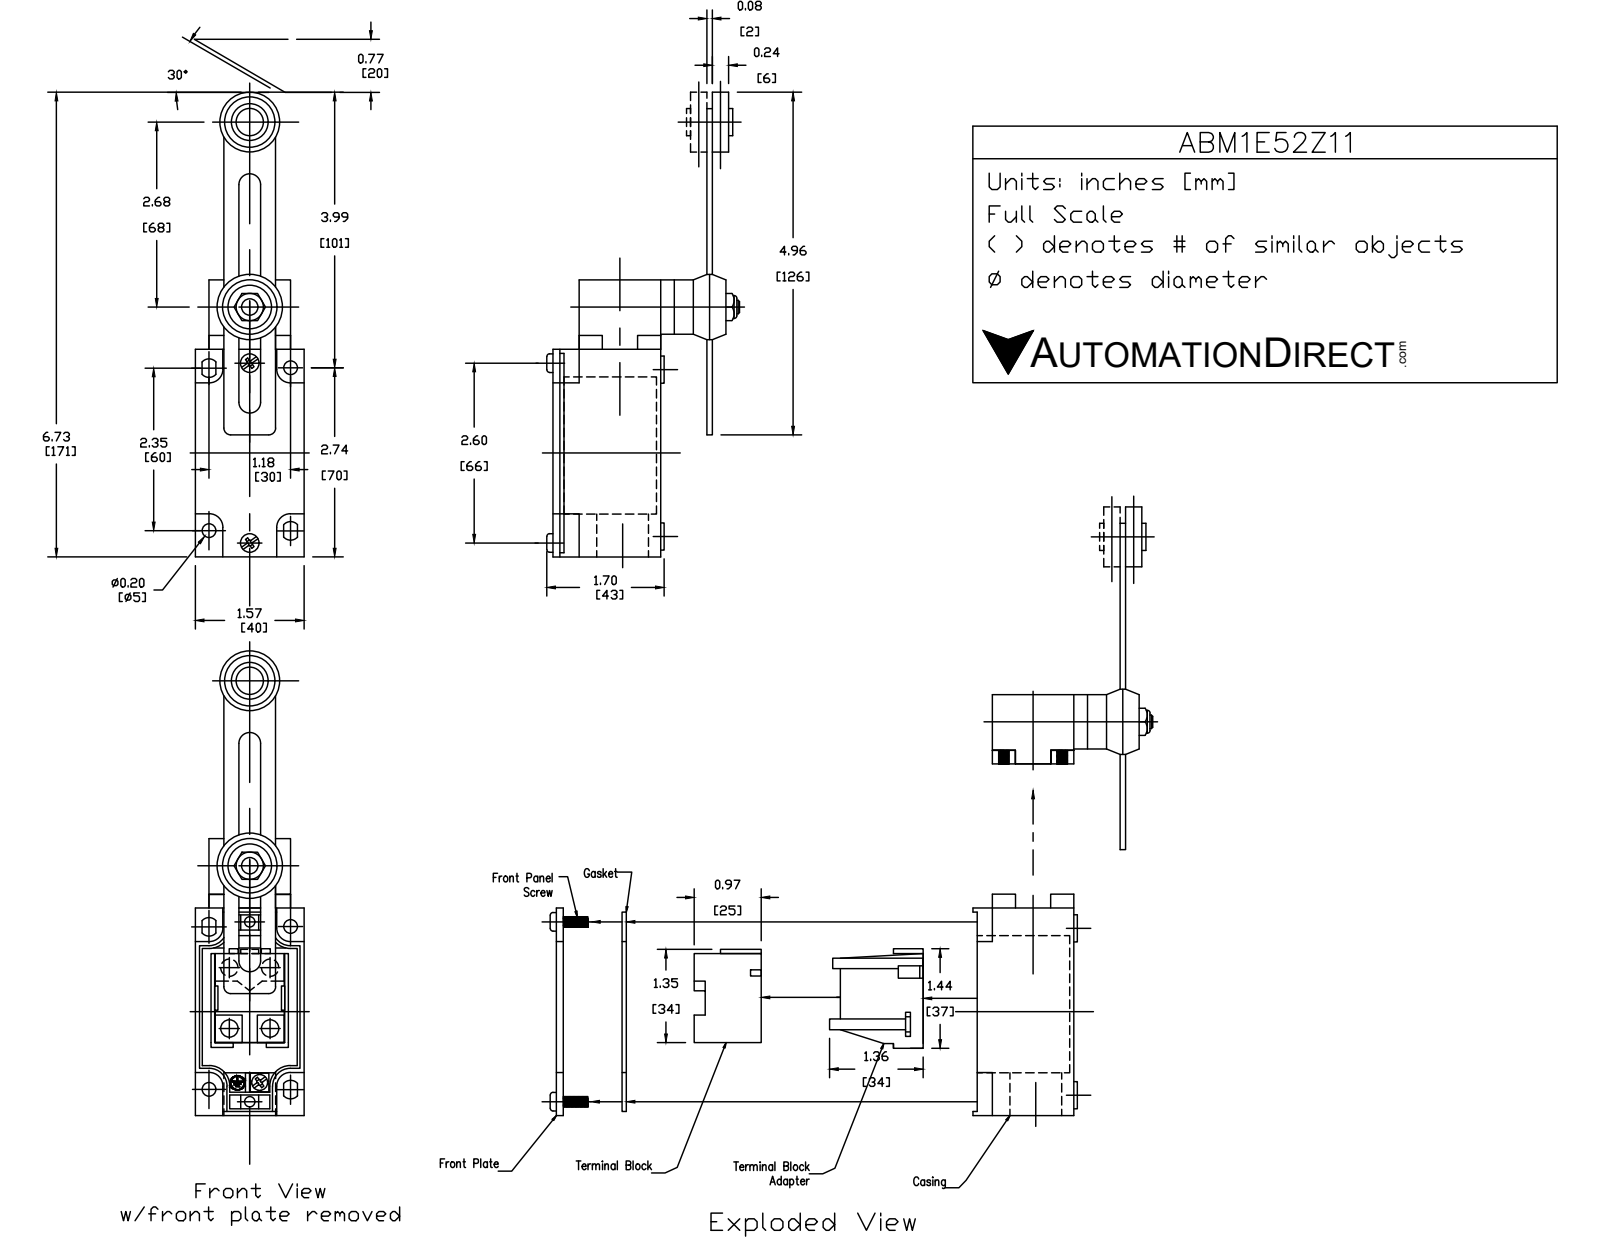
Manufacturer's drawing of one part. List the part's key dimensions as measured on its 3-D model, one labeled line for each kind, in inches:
Part name (STEP PRODUCT): ABM1E52Z11
STEP written by: SolidWorks 2017 (AUTOMOTIVE_DESIGN)
Units: inches
Bodies: 5 solids, 277 faces (131 planar, 109 cylindrical, 37 other)
Overall size (bounding box): 6.535 × 2.35 × 1.575
Volume: 8.878 in³ · Surface area: 51.08 in²
Round holes (diameter × count): ⌀0.205 ×2, ⌀0.118 ×1, ⌀0.236 ×1, ⌀0.551 ×1, ⌀0.669 ×1, ⌀0.748 ×1
Round bosses / shafts (diameter × count): ⌀0.394 ×6, ⌀0.276 ×3, ⌀0.945 ×1, ⌀0.866 ×1, ⌀0.787 ×1, ⌀0.453 ×1, ⌀0.236 ×1
Partial cylindrical surfaces — rounded edges, fillets, slot ends (radius × count): R0.059 ×16, R0.039 ×4, R0.197 ×4, R0.118 ×2, R0.128 ×2, R0.159 ×2, R0.276 ×1, R0.453 ×1
Main face-to-face distances: 1.575, 1.555, 0.197, 1.181, 0.079, 0.323, 1.878, 0.402, 1.957, 1.378
Hole centre spacings: 0.551, 1.048, 2.641, 3.282
